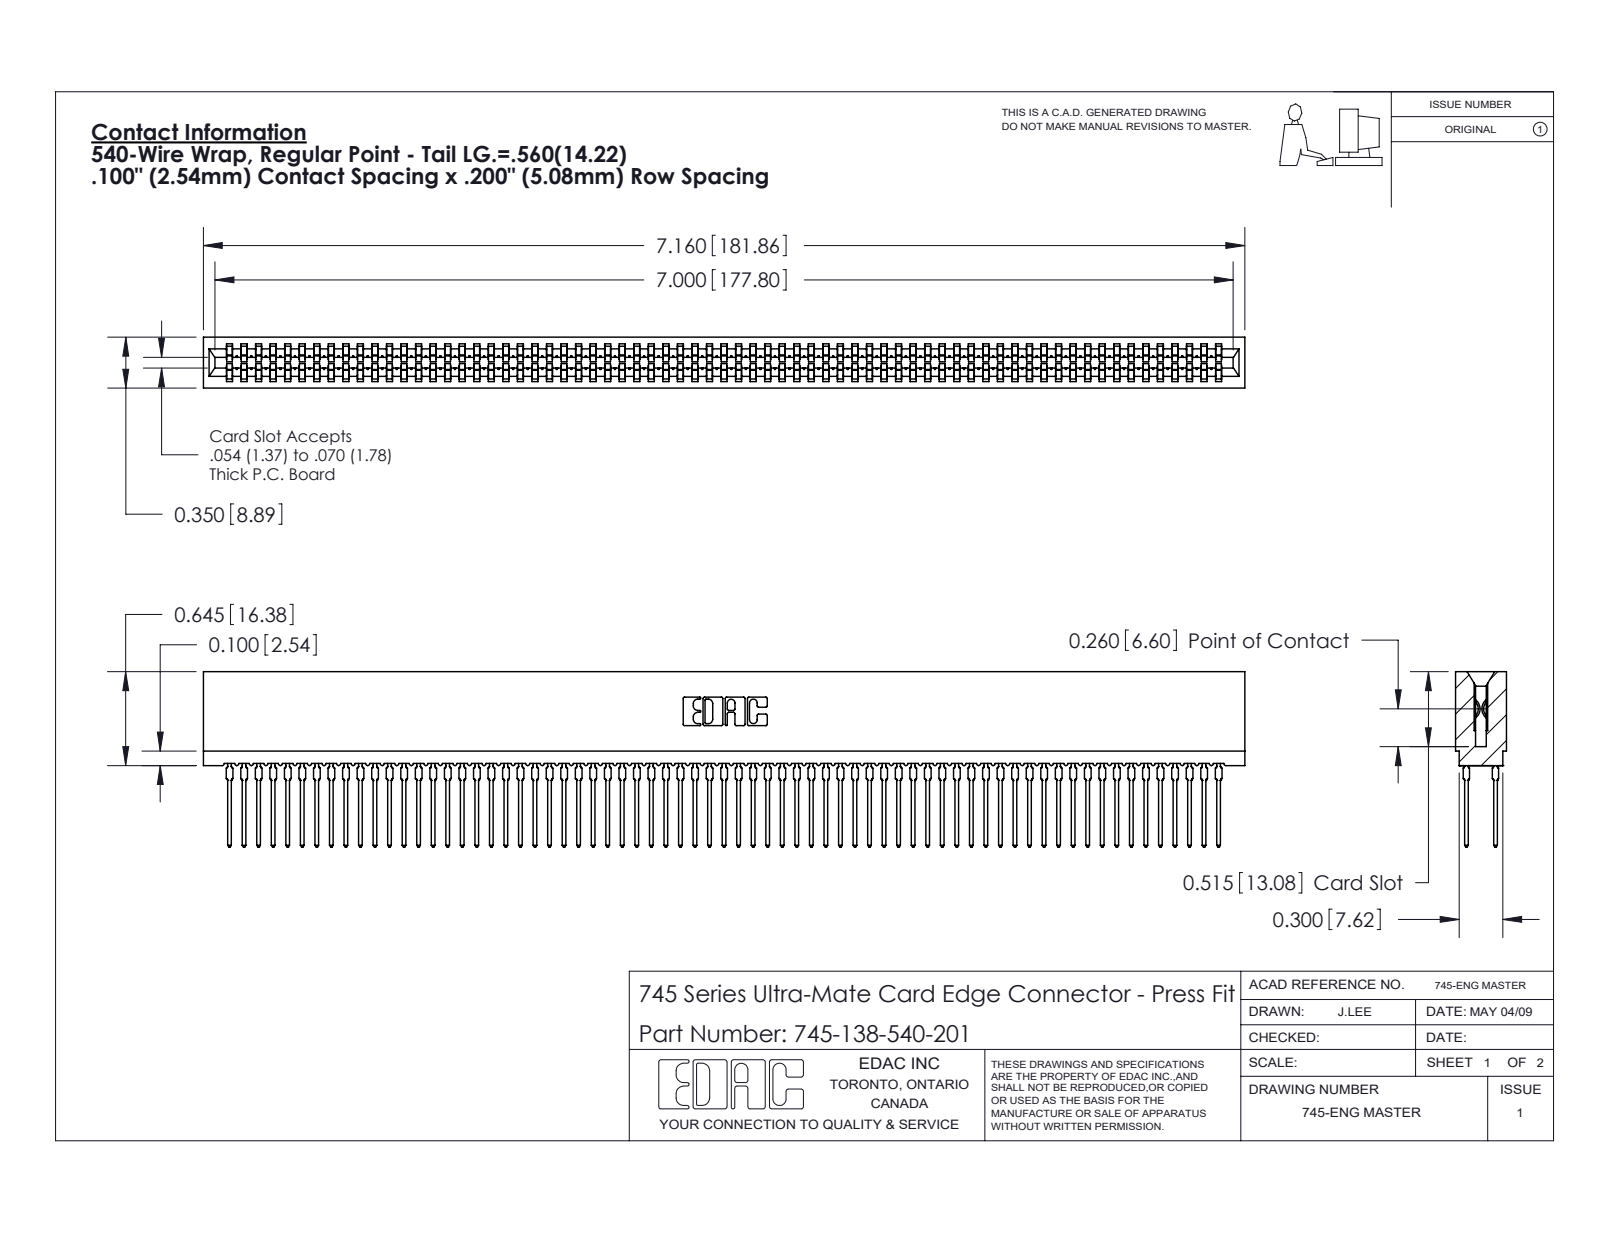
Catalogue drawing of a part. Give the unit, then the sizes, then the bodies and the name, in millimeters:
Units: millimetres
Overall size (bounding box): 181.9 × 30.6 × 8.9
Partial cylindrical surfaces — rounded edges, fillets, slot ends (radius × count): R0.5 ×276, R0.4 ×138, R0.3 ×22, R0.1 ×8, R0.3 ×8, R0.2 ×6, R0.8 ×6, R0.7 ×3
Main face-to-face distances: 1.6, 7.3, 8.9, 1.1, 7.7, 0.5, 6.2, 3.5, 5.4, 2.4
Volume: 16 620 mm³ · Surface area: 36 010 mm²
Bodies: 139 solids, 12446 faces (6403 planar, 2455 cylindrical, 3588 other)
Part name (STEP PRODUCT): 745-292-001_540; 745 Part_Insulator Option - 01; 745-138-540-201
STEP written by: SolidWorks 2020 (CONFIG_CONTROL_DESIGN)
